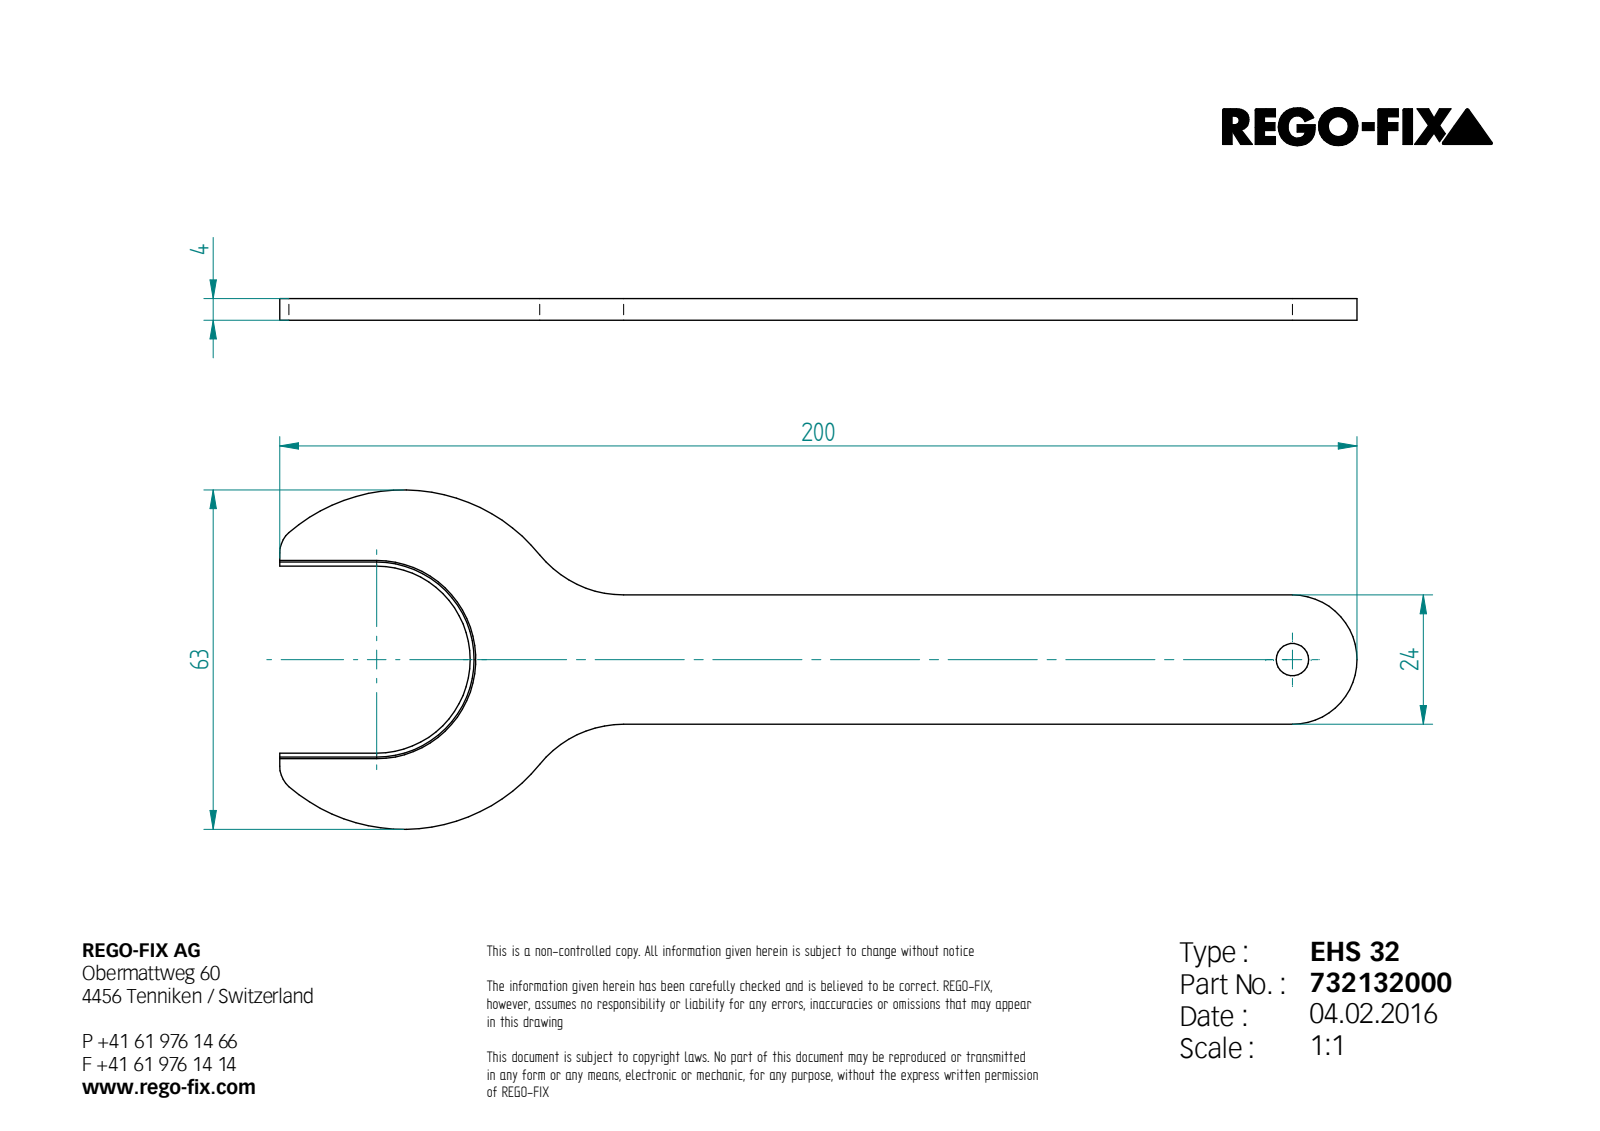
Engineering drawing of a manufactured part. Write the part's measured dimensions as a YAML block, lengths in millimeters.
step_written_by: "Unknown (AUTOMOTIVE_DESIGN)"
units: millimeters
bodies: {solids: 1, faces: 26, planar: 14, cylindrical: 10, other: 2}
overall_size: [200, 63, 4]
volume: 20733
surface_area: 12626
round_holes:
  - {diameter: 6, count: 1}
partial_cylinders:
  - {radius: 5, count: 2}
  - {radius: 20, count: 2}
  - {radius: 32.5, count: 2}
  - {radius: 12, count: 1}
  - {radius: 17.35, count: 1}
  - {radius: 18.1, count: 1}
face_to_face_distances: [4, 24, 6.1, 30.1, 36.2, 1.91, 0.75, 35.45, 5.35, 29.35]
